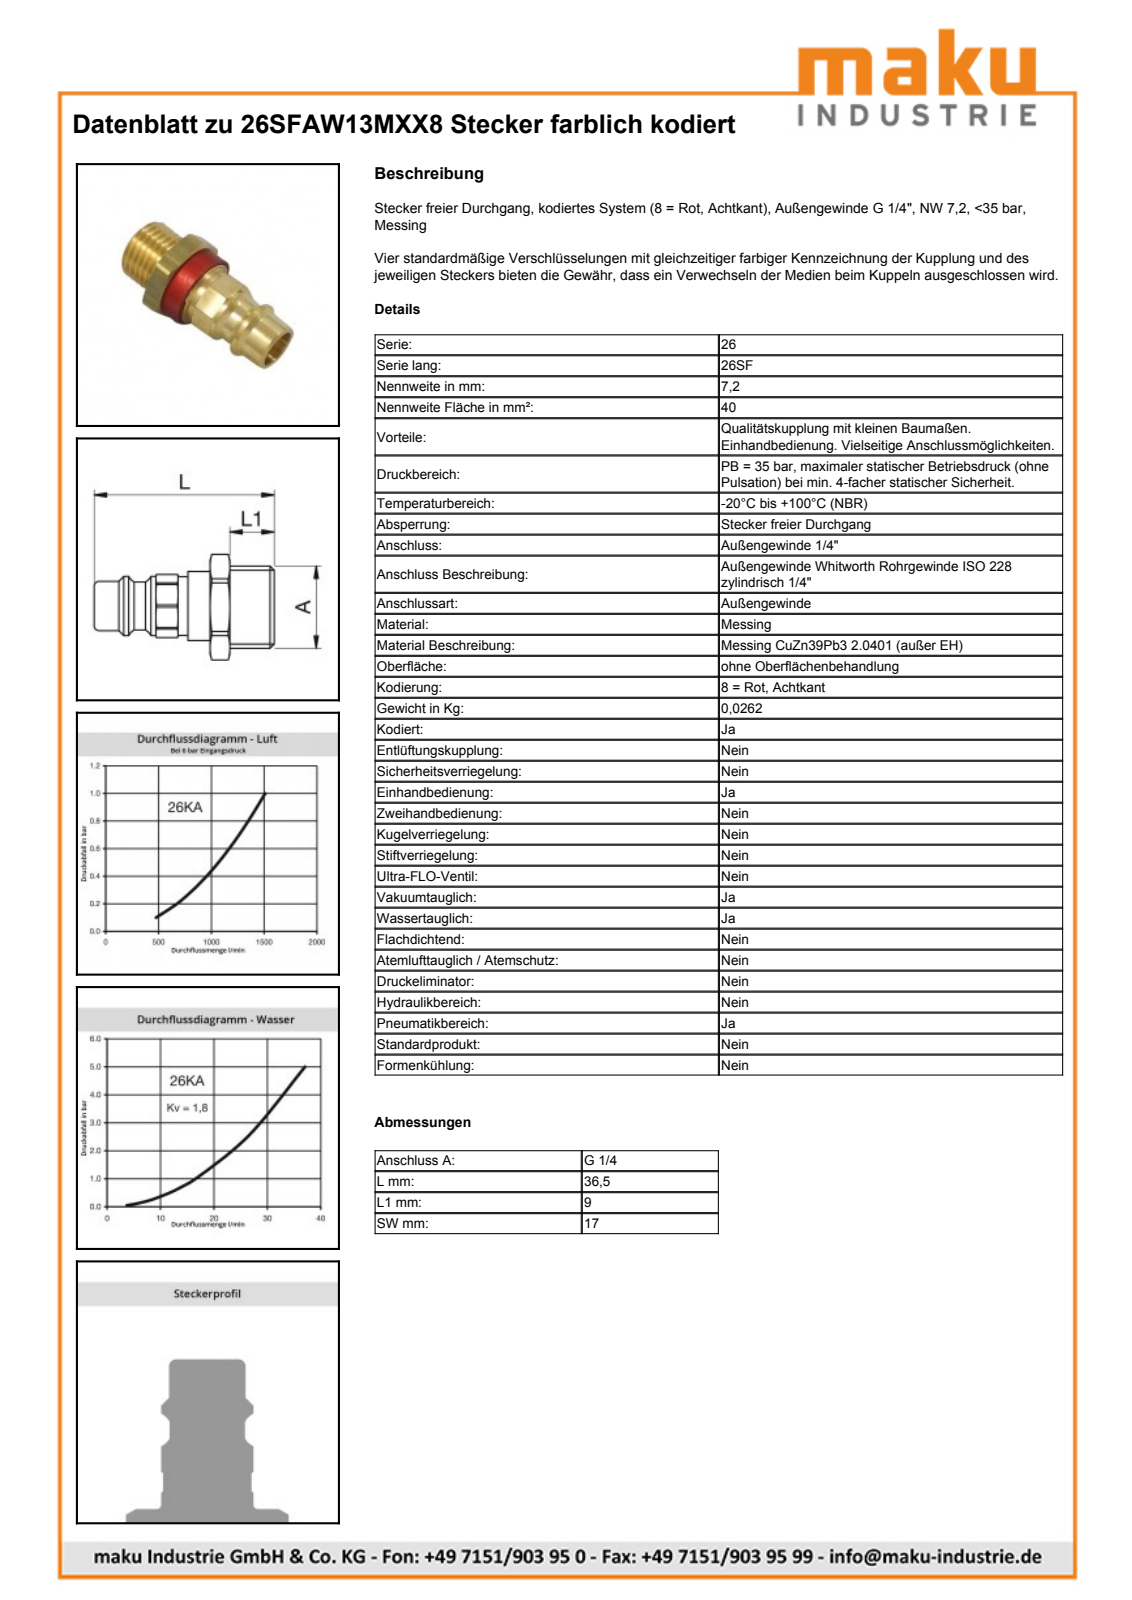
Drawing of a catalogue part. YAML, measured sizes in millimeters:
part_name: "D107821; D107820; D103012"
step_written_by: "Autodesk Inventor 2013 (AUTOMOTIVE_DESIGN)"
units: millimeters
bodies: {solids: 2, faces: 86, planar: 21, cylindrical: 25, other: 40}
overall_size: [36.5, 19.15, 17]
volume: 3092
surface_area: 3177
round_holes:
  - {diameter: 7.85, count: 1}
  - {diameter: 13.85, count: 1}
  - {diameter: 14.05, count: 1}
round_bosses_or_shafts:
  - {diameter: 15.5, count: 1}
  - {diameter: 14, count: 1}
  - {diameter: 13.16, count: 1}
  - {diameter: 12, count: 1}
  - {diameter: 11.9, count: 1}
  - {diameter: 10, count: 1}
  - {diameter: 9.75, count: 1}
partial_cylinders:
  - {radius: 6.4, count: 1}
  - {radius: 9.57, count: 1}
face_to_face_distances: [17, 4, 12, 2.5, 14.5, 4.5, 8.5, 17.5, 13, 9]
